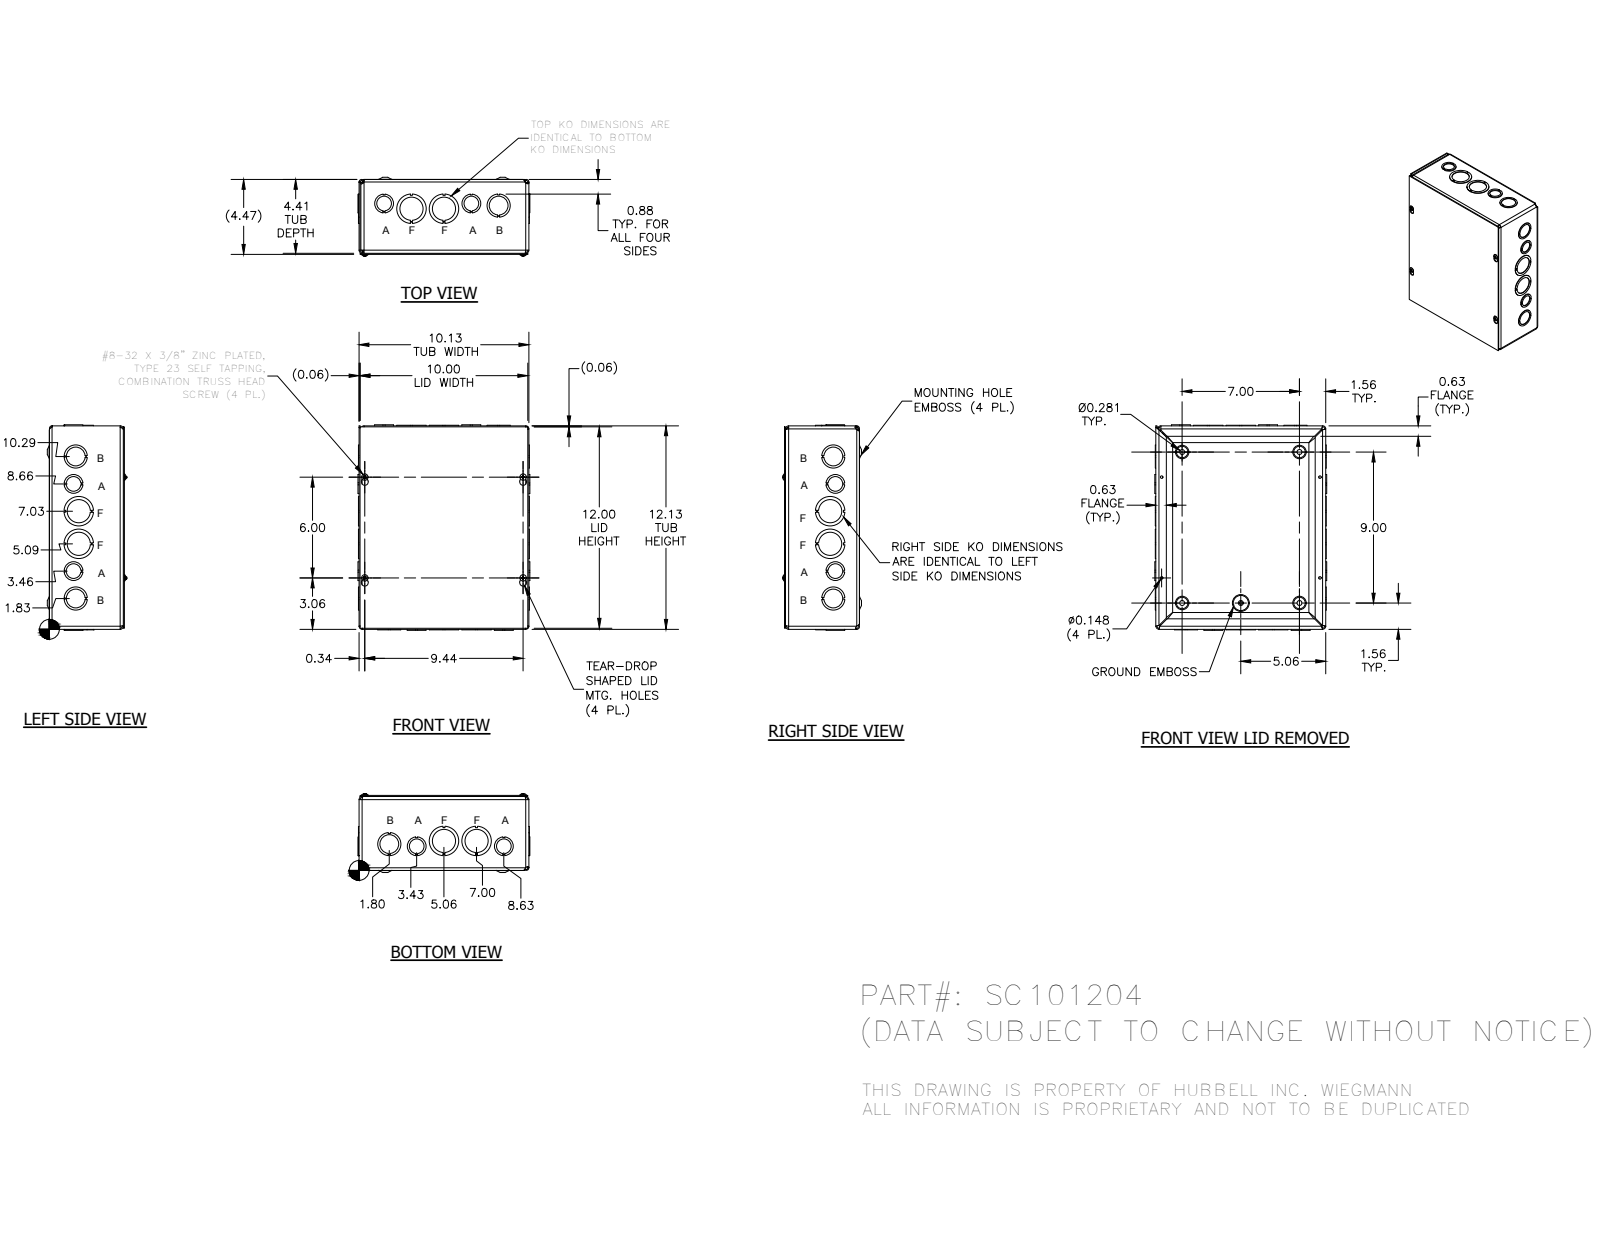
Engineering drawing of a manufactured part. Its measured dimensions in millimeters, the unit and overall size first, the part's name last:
Units: millimetres
Overall size (bounding box): 311.12 × 260.32 × 119.2
Round holes (diameter × count): ⌀28.57 ×10, ⌀34.92 ×9, ⌀22.22 ×6, ⌀44.45 ×5, ⌀3.76 ×4, ⌀7.62 ×4, ⌀4.19 ×1
Round bosses / shafts (diameter × count): ⌀9.75 ×4, ⌀4.17 ×4, ⌀5.8 ×1
Partial cylindrical surfaces — rounded edges, fillets, slot ends (radius × count): R3.17 ×12, R4.75 ×8, R1.4 ×4, R1.57 ×4, R2.38 ×4, R2.97 ×4, R3.15 ×4, R3.96 ×4
Main face-to-face distances: 1.57, 110.32, 111.89, 1.59, 111.91, 113.48, 1.58, 257.18, 255.6, 255.61
Hole centre spacings: 42.15, 91.03, 49.09, 49.28, 132.17, 193, 282.61, 41.52
Bodies: 22 solids, 974 faces (617 planar, 199 cylindrical, 158 other)
Part name (STEP PRODUCT): SC1012BKP; SC101204WRA; SC1012LID; 34056 (+1 more)
STEP written by: Autodesk Inventor 2014 (AUTOMOTIVE_DESIGN)
